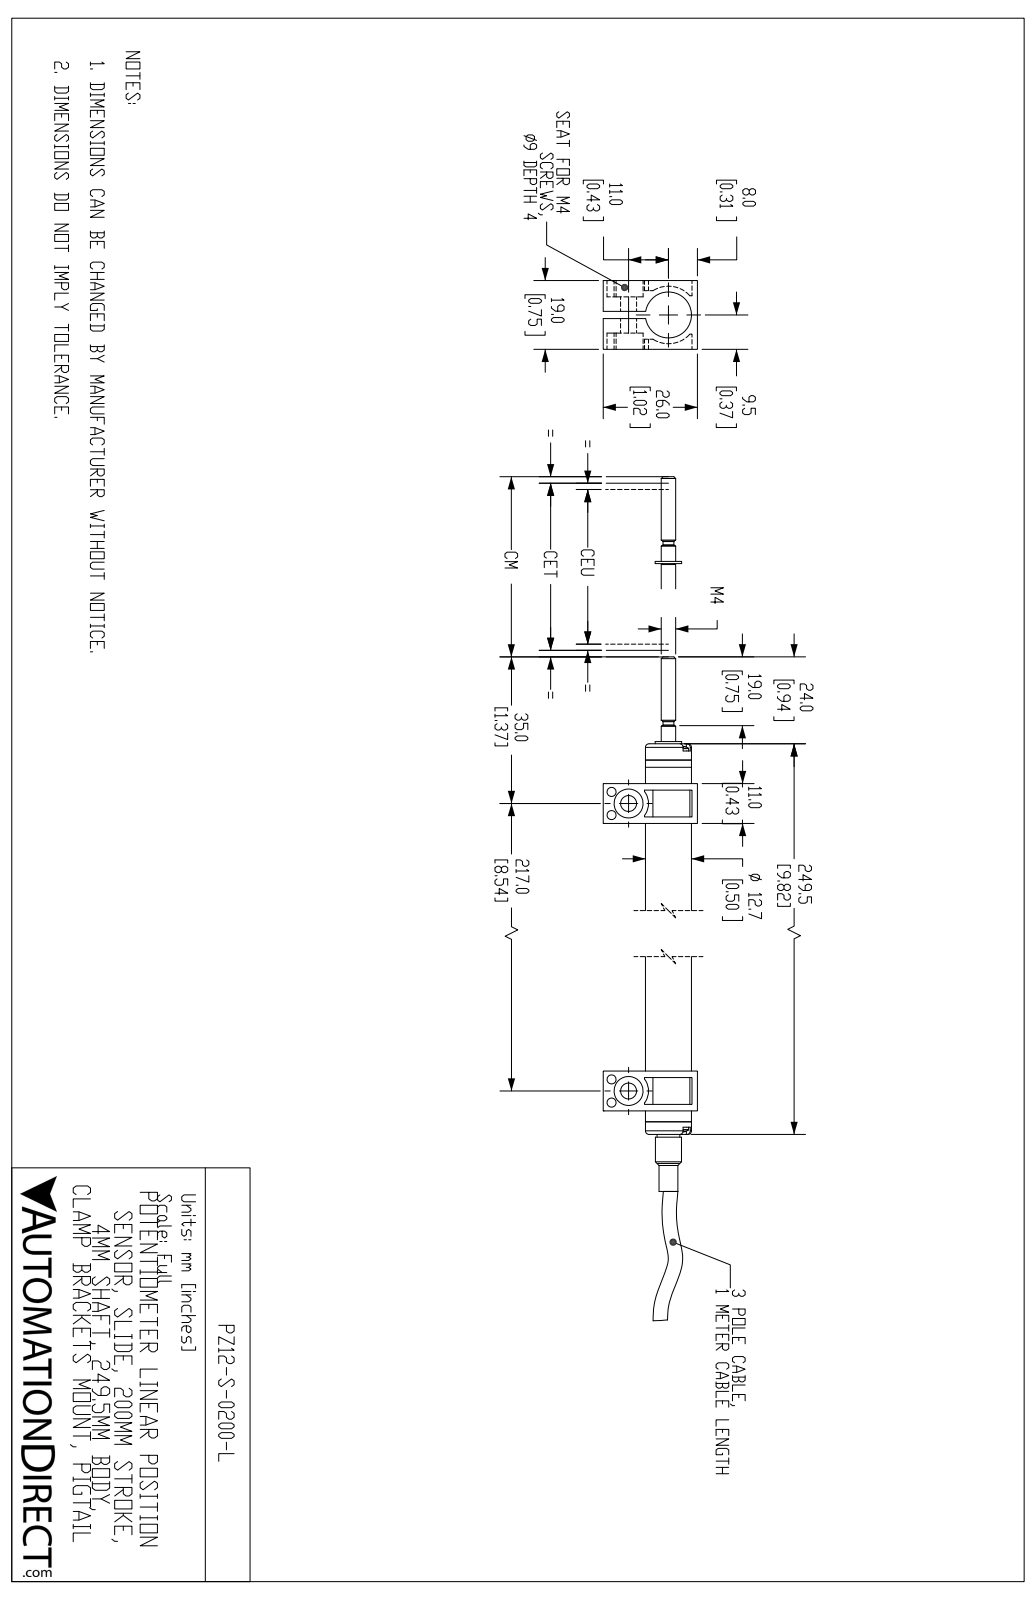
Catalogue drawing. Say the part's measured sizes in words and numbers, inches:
The part is named "PZ12-S-0200-L". Its 3-D file was written by "SolidWorks 2019 (AUTOMOTIVE_DESIGN)". It is 14 solids with 586 faces: 198 planar, 164 cylindrical and 224 other. Overall it measures 12.793 by 1.024 by 0.748 inches. Its volume is 2.444 cubic inches and its surface area 37.27 square inches. Round holes: 4 of diameter 0.098, 2 of diameter 0.055, 2 of diameter 0.059, 2 of diameter 0.079, 2 of diameter 0.173, 2 of diameter 0.315, 1 of diameter 0.039, 1 of diameter 0.126, 1 of diameter 0.138, 1 of diameter 0.201, 1 of diameter 0.219, 1 of diameter 0.236. Round bosses or shafts: 2 of diameter 0.126, 2 of diameter 0.063, 2 of diameter 0.02, 1 of diameter 0.5, 1 of diameter 0.283, 1 of diameter 0.248, 1 of diameter 0.205, 1 of diameter 0.157. Partial cylindrical surfaces (rounded edges, fillets, slot ends): 4 of radius 0.01, 2 of radius 0.02, 2 of radius 0.026, 2 of radius 0.069, 2 of radius 0.217, 1 of radius 0.017, 1 of radius 0.103, 1 of radius 0.144. The main face-to-face distances are 8.681, 0.433, 0.177, 0.079, 0.335, 0.413, 0.571, 9.114, 1.024, 8.248. The hole center spacings are 0.224, 8.681, 0.189, 0.197, 0.213, 0.252, 0.322, 8.557.
